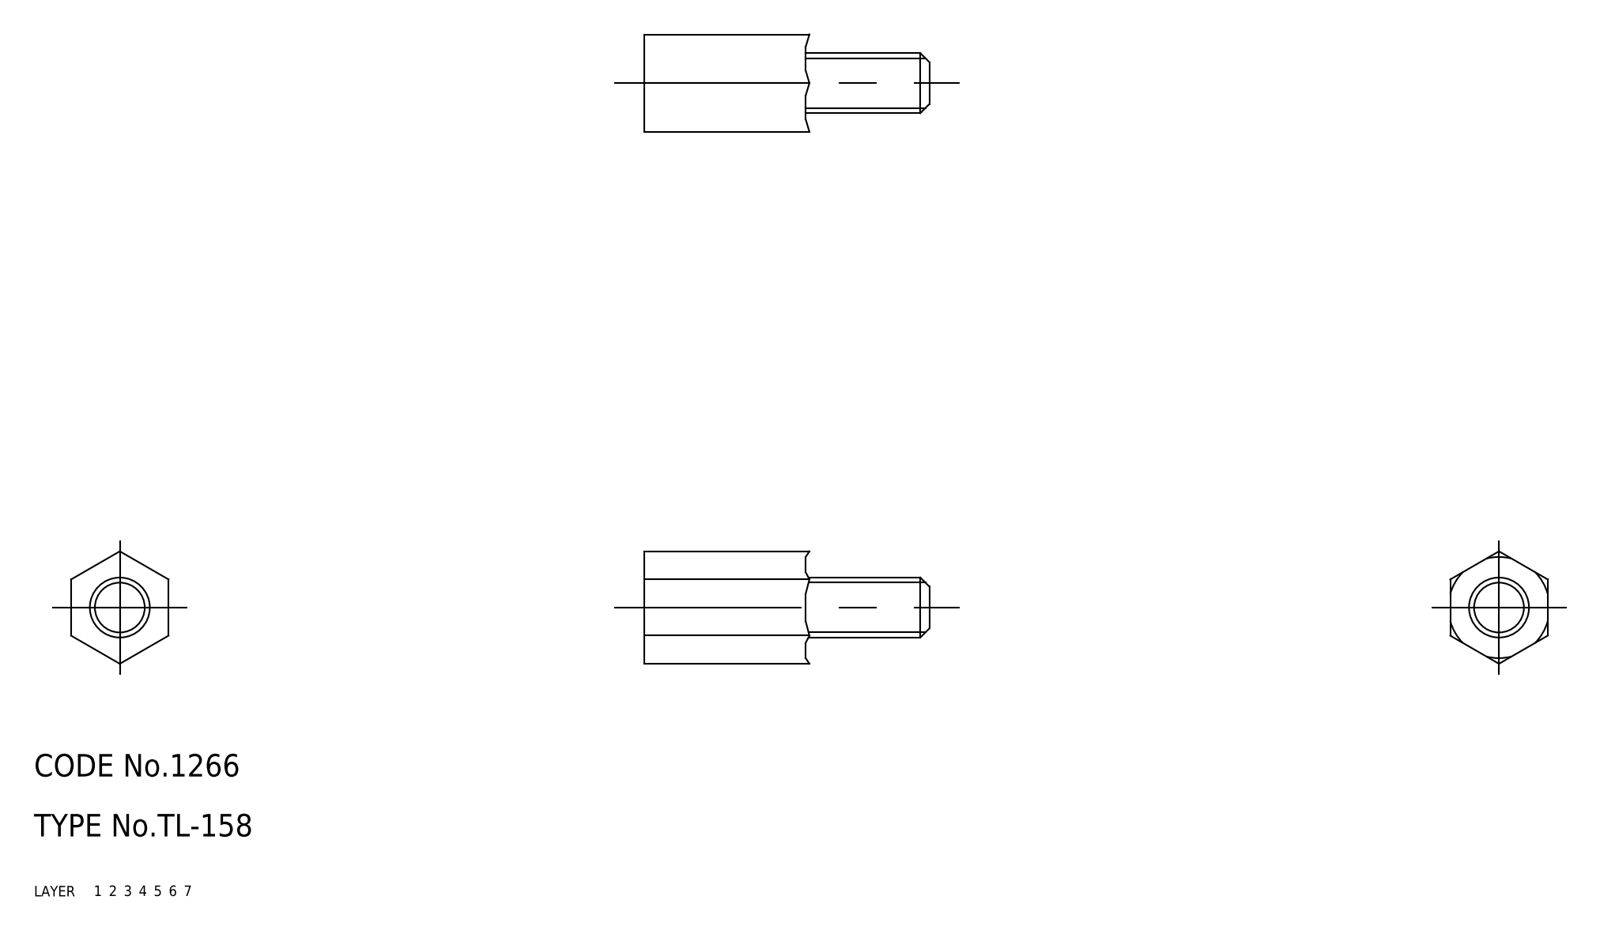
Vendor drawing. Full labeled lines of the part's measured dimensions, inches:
Part name (STEP PRODUCT): nut
STEP written by: CADfix (AUTOMOTIVE_DESIGN)
Units: inches
Bodies: 1 solid, 22 faces (0 planar, 0 cylindrical, 22 other)
Overall size (bounding box): 1.496 × 0.591 × 0.512
Volume: 0.199 in³ · Surface area: 3.123 in²
